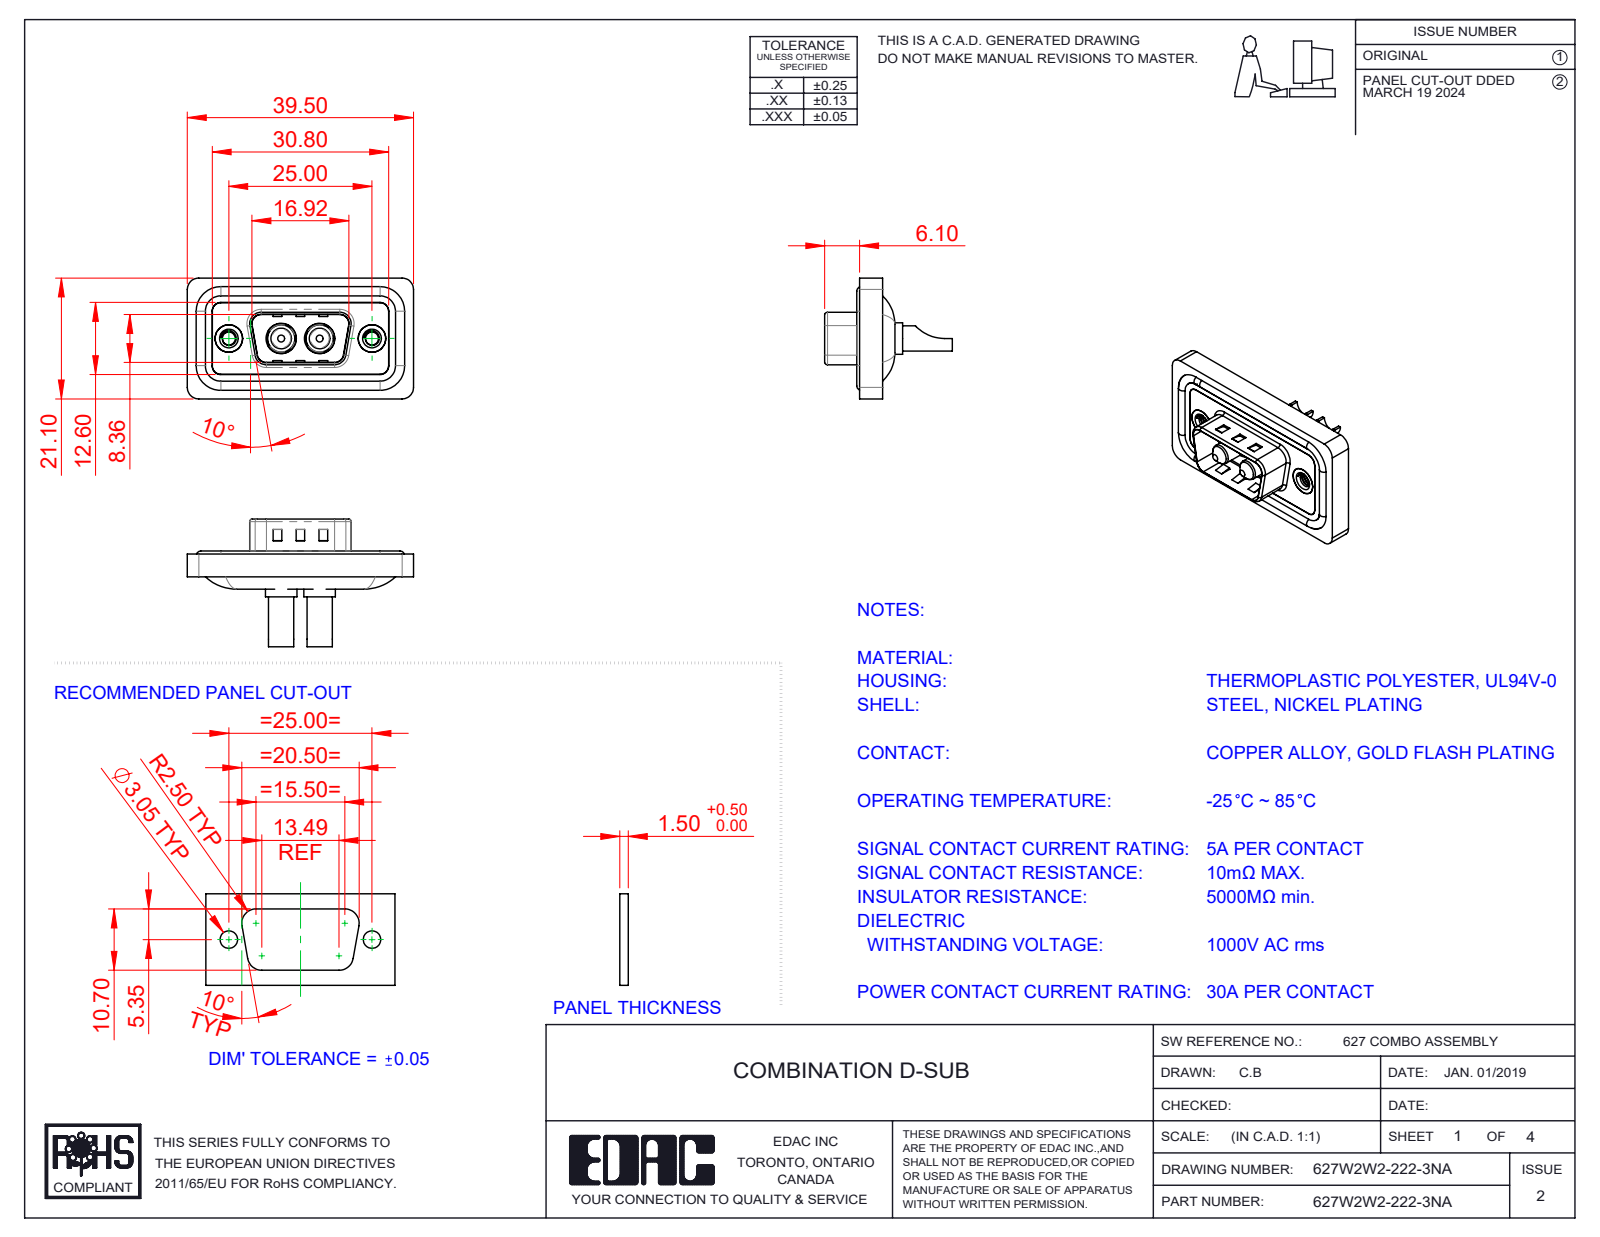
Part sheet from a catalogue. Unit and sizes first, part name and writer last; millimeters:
Units: millimetres
Overall size (bounding box): 39.5 × 22.3 × 21.1
Round holes (diameter × count): ⌀2.26 ×2, ⌀3.5 ×2, ⌀4 ×2, ⌀4.8 ×2, ⌀4.85 ×2, ⌀5 ×2, ⌀5.3 ×2
Round bosses / shafts (diameter × count): ⌀1.6 ×4, ⌀5.5 ×2, ⌀5.2 ×2, ⌀4.9 ×2, ⌀4.75 ×2, ⌀4.4 ×2, ⌀3.75 ×2, ⌀3.6 ×2
Partial cylindrical surfaces — rounded edges, fillets, slot ends (radius × count): R1.5 ×22, R2 ×18, R0.5 ×8, R1.6 ×8, R0.25 ×4, R0.6 ×4, R0.65 ×4, R0.9 ×4
Main face-to-face distances: 0.4, 1.1, 2.9, 3.1, 0.5, 1.6, 1.5, 2.5, 4, 0.7
Hole centre spacings: 9.14, 15.86, 6.72, 25
Volume: 4 510 mm³ · Surface area: 7 197 mm²
Bodies: 11 solids, 499 faces (171 planar, 226 cylindrical, 102 other)
Part name (STEP PRODUCT): 627Combo Shell Front_09 Contacts; 627Combo Shell Rear_09 Contacts; 627Combo Waterproof Housing_09 Contacts; 627Combo Housing_2W2 (+3 more)
STEP written by: SolidWorks 2023 (CONFIG_CONTROL_DESIGN)
